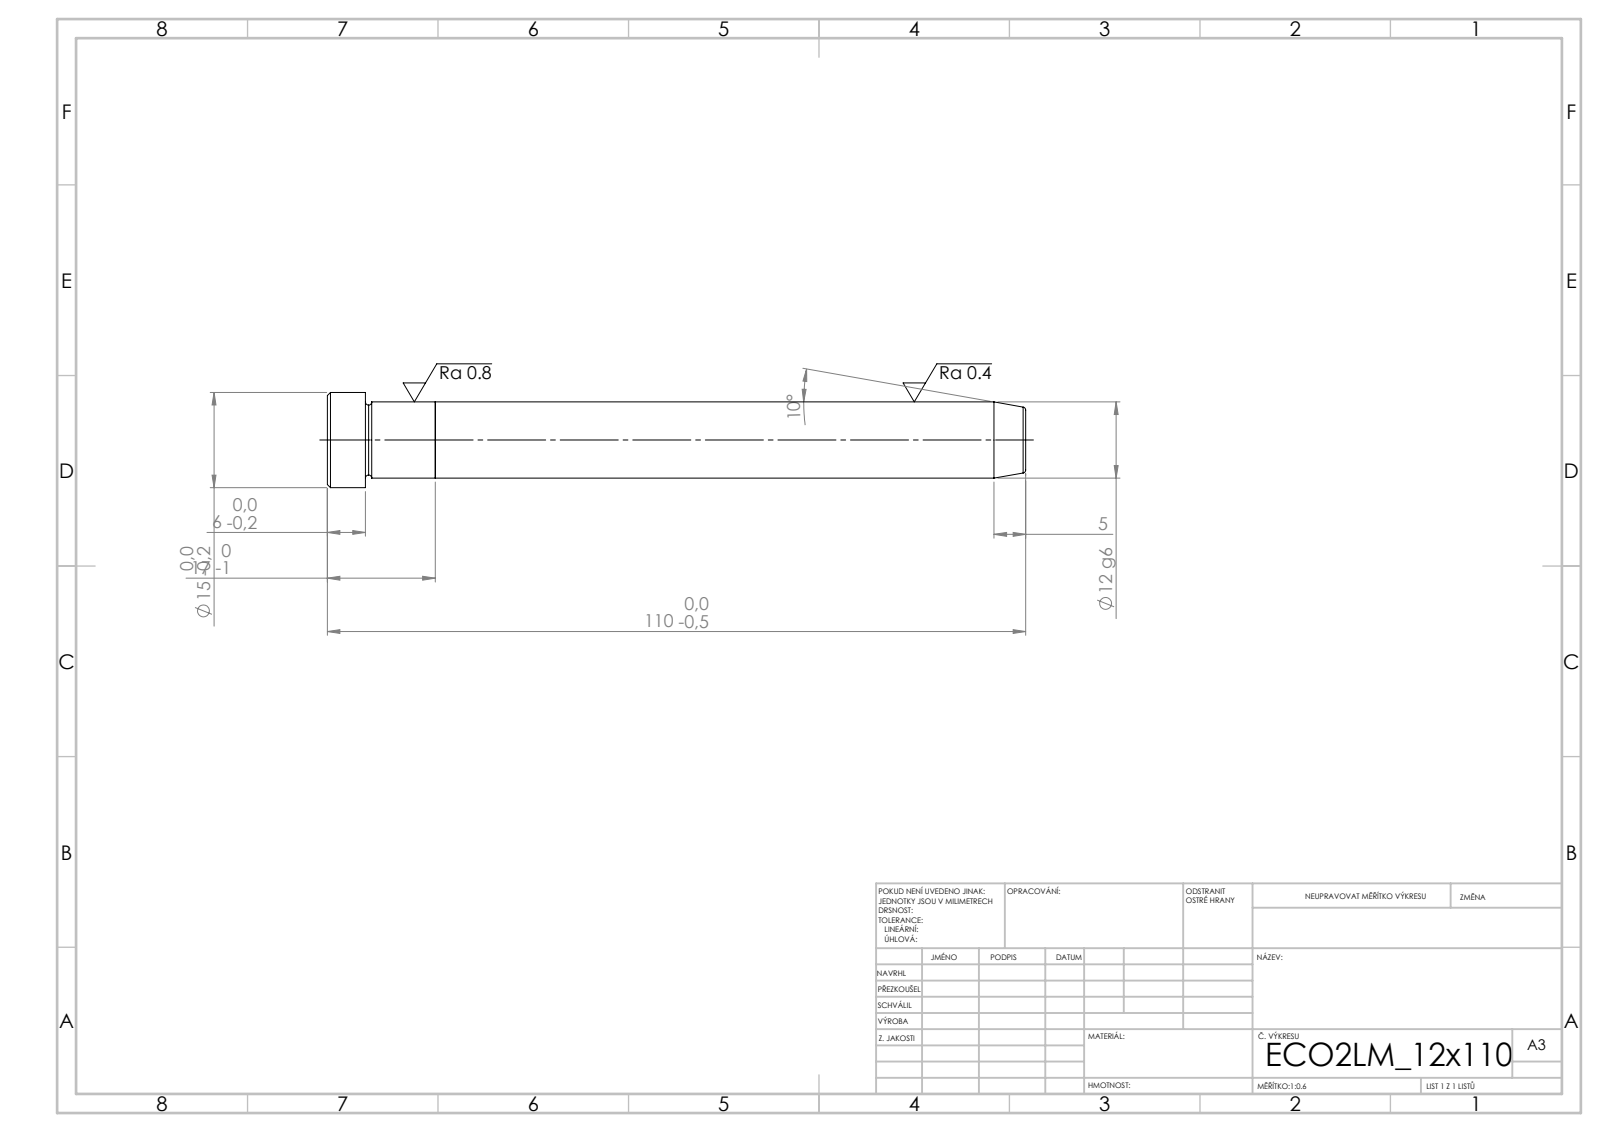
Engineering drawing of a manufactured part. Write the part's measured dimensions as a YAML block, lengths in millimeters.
step_written_by: "SolidWorks 2019 (CONFIG_CONTROL_DESIGN)"
units: millimeters
bodies: {solids: 2, faces: 21, planar: 5, cylindrical: 6, other: 10}
overall_size: [110, 15, 15]
volume: 12722
surface_area: 4741
round_bosses_or_shafts:
  - {diameter: 15, count: 1}
  - {diameter: 12, count: 1}
face_to_face_distances: [17, 93, 110, 104, 11, 6]
